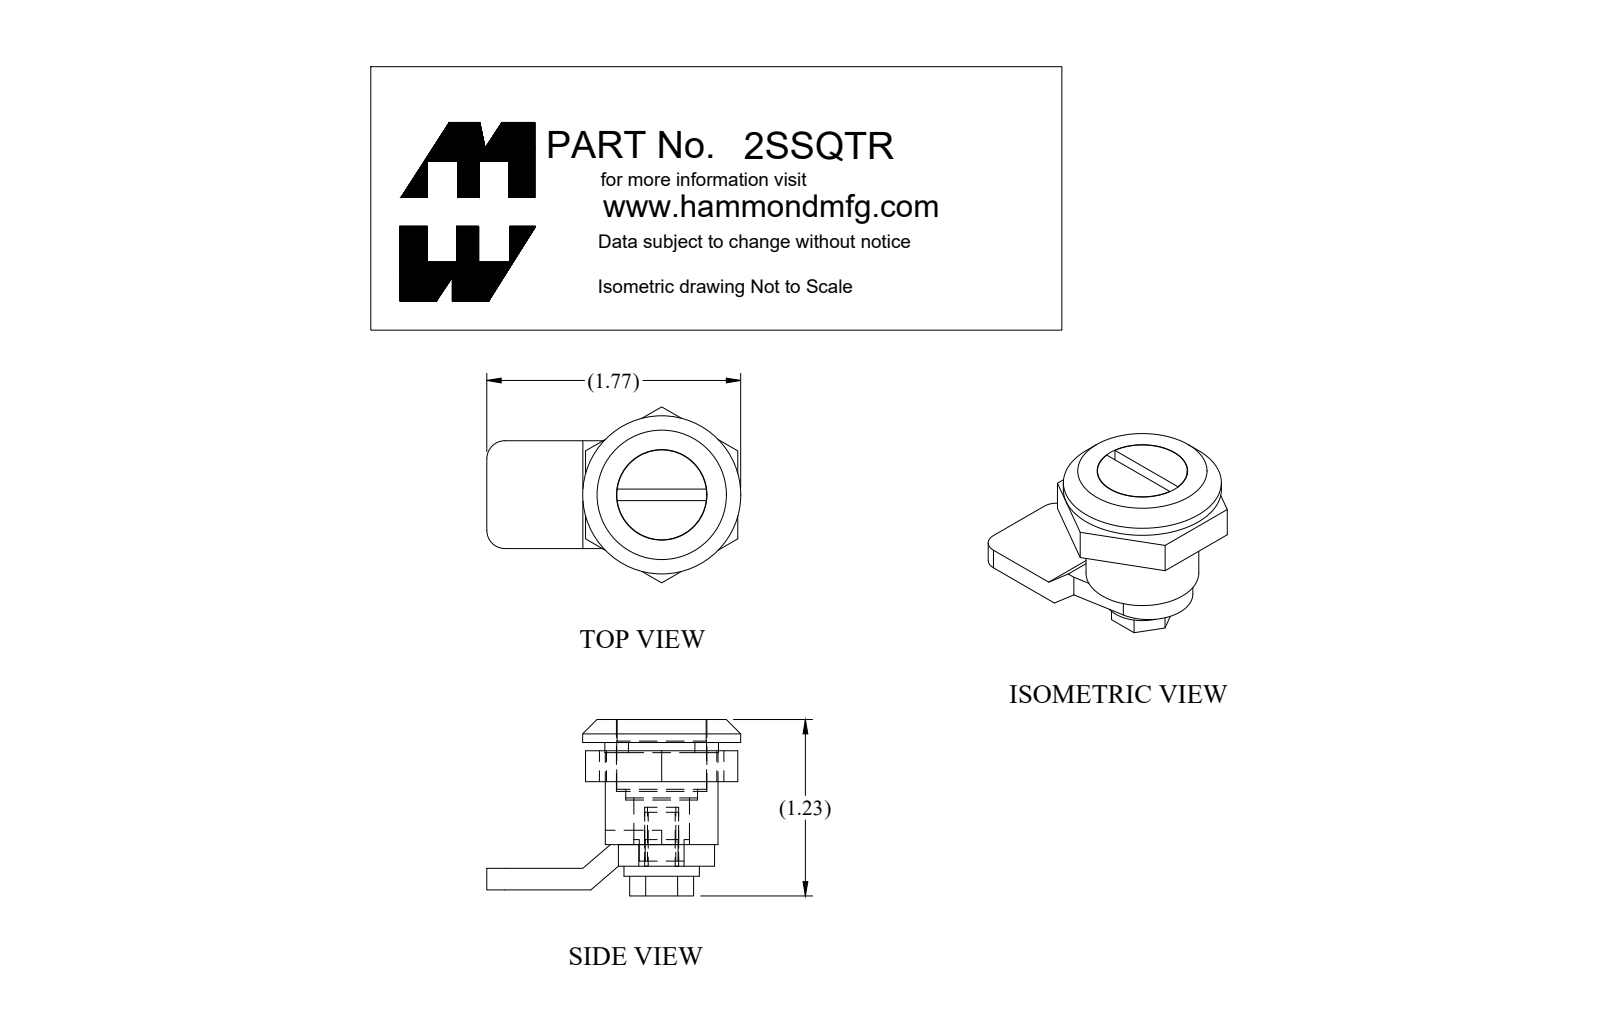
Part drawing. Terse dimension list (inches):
name: 2SSQTR
written by: SolidWorks 2018 (AUTOMOTIVE_DESIGN)
unit: in
bodies: 5 solids, 83 faces (67 planar, 15 cylindrical, 1 other)
size: 1.768 × 1.227 × 1.224
volume: 0.775 in³; area: 13.98 in²
holes: 1× ⌀0.197, 1× ⌀0.387, 1× ⌀0.5, 1× ⌀0.63, 1× ⌀0.768
bosses: 1× ⌀1.1, 1× ⌀0.785, 1× ⌀0.625, 1× ⌀0.525, 1× ⌀0.236
rounds: 2× R0.125, 1× R0.307
face distances: 0.15, 0.015, 0.87, 0.315, 1.185, 0.968, 0.653, 0.217, 0.753, 0.438
